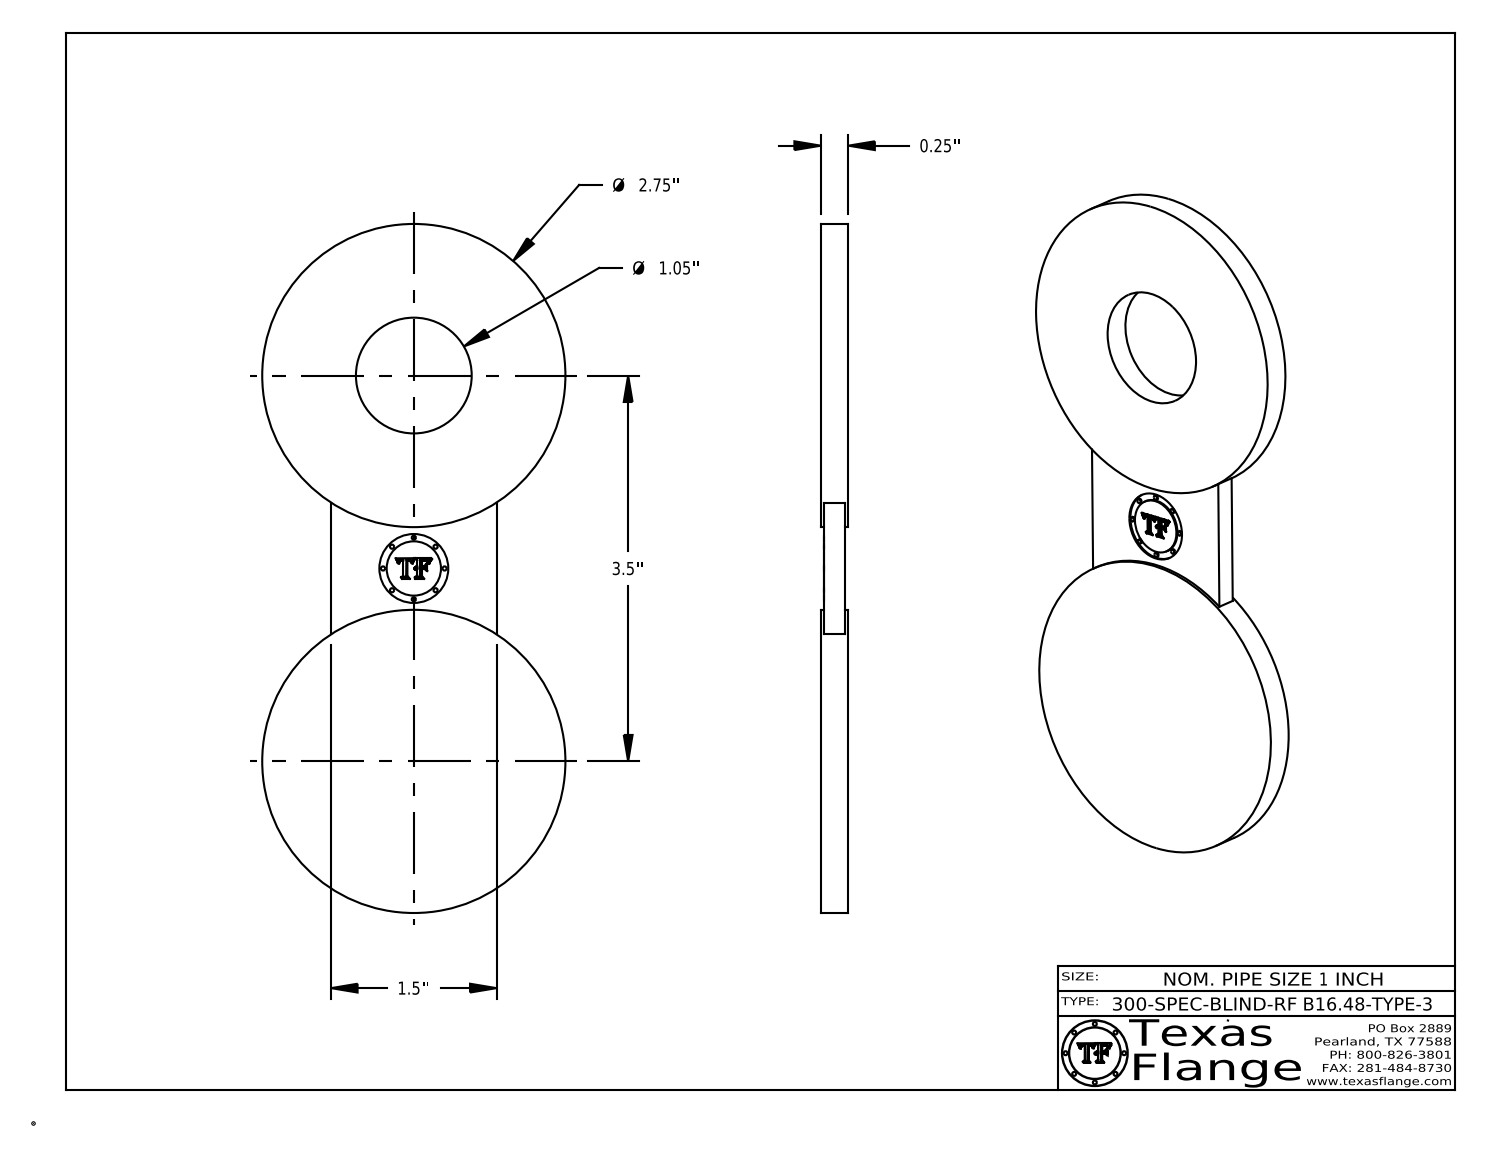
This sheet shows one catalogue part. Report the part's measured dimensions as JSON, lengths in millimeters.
{"part_name": "1-300-SPEC-BLIND-RF-B16.48-TYPE-3", "step_written_by": "CATIA V5 STEP AP214 (AUTOMOTIVE_DESIGN)", "units": "millimeters", "bodies": {"solids": 1, "faces": 399, "planar": 373, "cylindrical": 26, "other": 0}, "overall_size": [158.8, 69.9, 6.4], "volume_mm3": 49210, "surface_area_mm2": 19240, "round_holes": [[15.9, 1], [26.7, 1]], "round_bosses_or_shafts": [[1, 8], [69.9, 2], [12.5, 1]], "face_to_face_distances": [6.4, 5.6, 0.8, 4.7, 38.1, 1.2, 5.2, 4.4, 0.4, 17.4], "hole_center_spacings": [44.5]}
